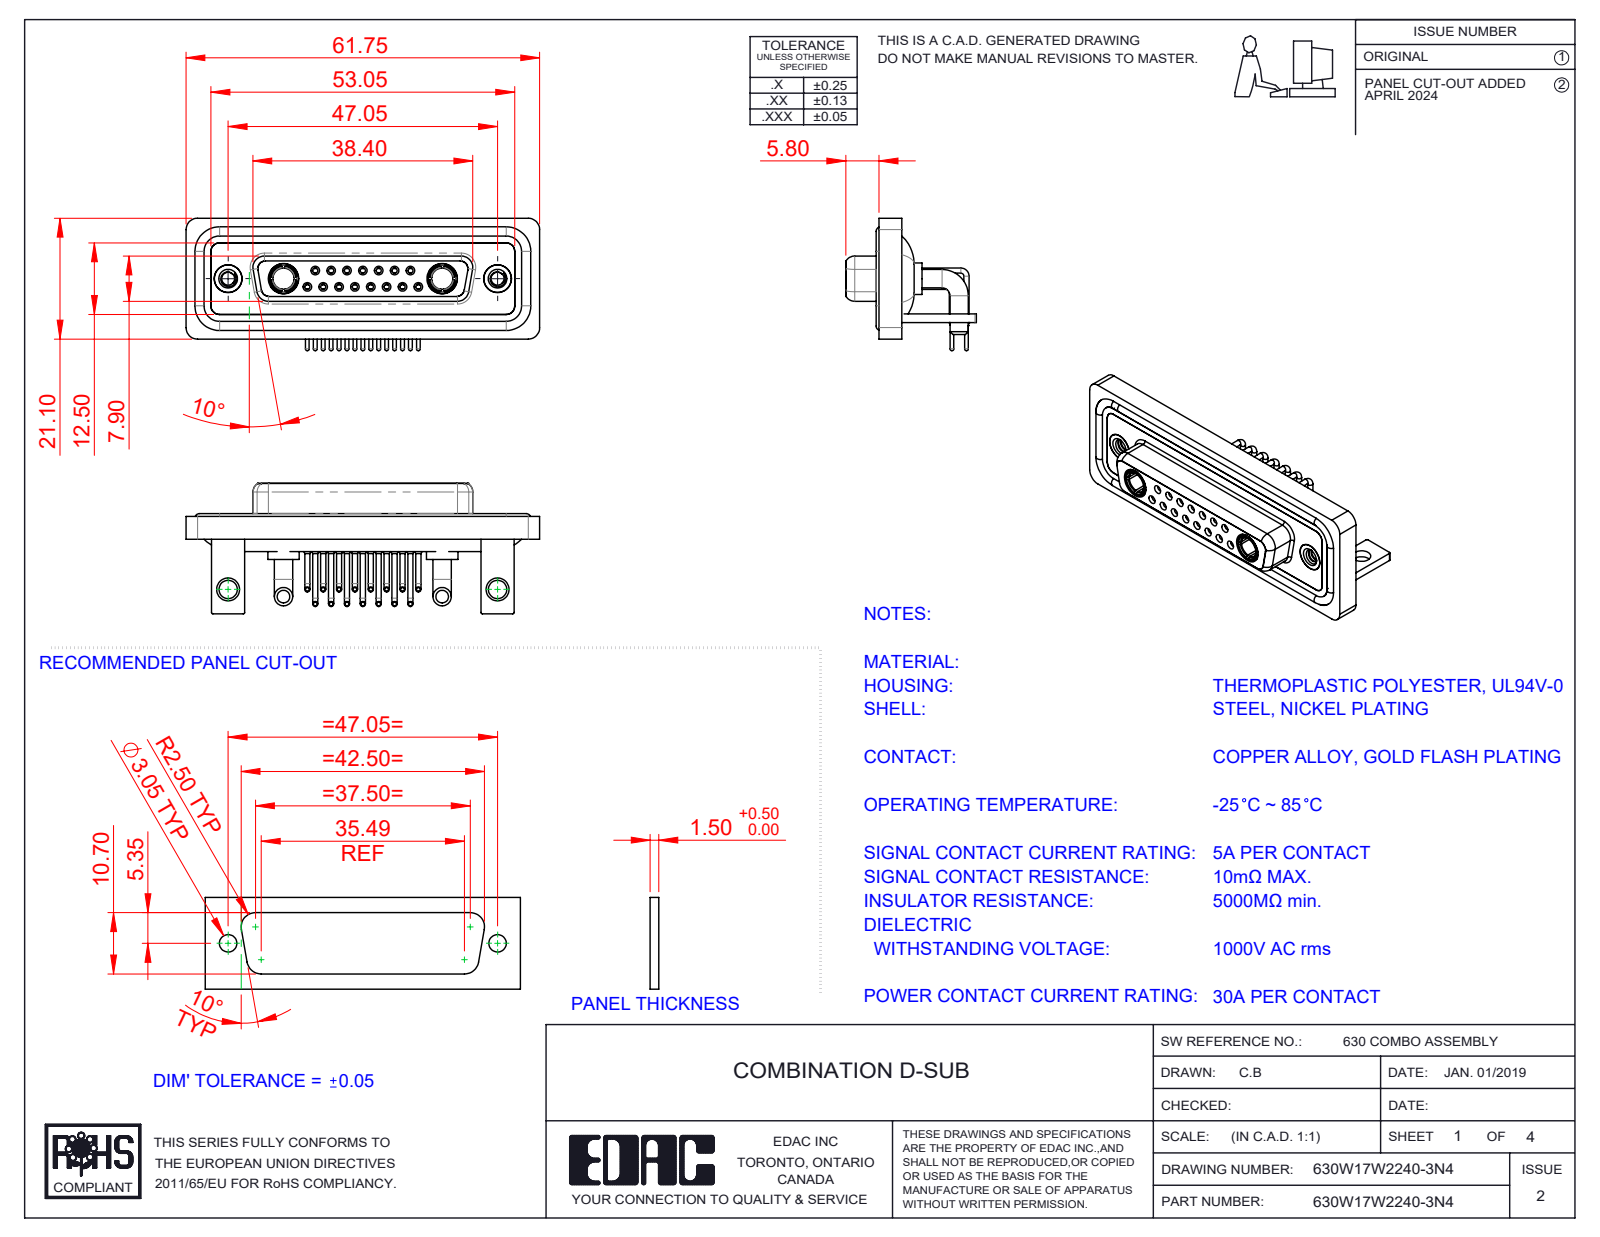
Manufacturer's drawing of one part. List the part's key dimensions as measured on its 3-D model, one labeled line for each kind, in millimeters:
Part name (STEP PRODUCT): 630Combo Shell Rear_25 Contacts; 630Combo Shell Front_25 Contacts; Power Socket_30A RA; 630Combo Contact Row 1_50 Contacts (+6 more)
STEP written by: SolidWorks 2023 (CONFIG_CONTROL_DESIGN)
Units: millimetres
Bodies: 28 solids, 1385 faces (408 planar, 607 cylindrical, 370 other)
Overall size (bounding box): 61.75 × 23.12 × 22.8
Volume: 8 909 mm³ · Surface area: 15 302 mm²
Round holes (diameter × count): ⌀0.9 ×15, ⌀1.1 ×15, ⌀1.5 ×15, ⌀2 ×15, ⌀1.6 ×8, ⌀1.7 ×7, ⌀4.85 ×4, ⌀2.26 ×2, ⌀3.2 ×2, ⌀3.7 ×2, ⌀4 ×2, ⌀4.05 ×2
Round bosses / shafts (diameter × count): ⌀0.9 ×15, ⌀0.65 ×15, ⌀1.6 ×11, ⌀3.2 ×4, ⌀5.5 ×2, ⌀5.2 ×2, ⌀4.96 ×2, ⌀4.95 ×2
Partial cylindrical surfaces — rounded edges, fillets, slot ends (radius × count): R2 ×19, R1.5 ×18, R0.25 ×16, R1.35 ×8, R1.6 ×8, R0.5 ×5, R0.6 ×4, R0.65 ×4
Main face-to-face distances: 0.4, 1.8, 2.9, 3.7, 1.5, 4.1, 1.1, 1.4, 1.6, 3.1
Hole centre spacings: 3.16, 2.77, 5.54, 8.31, 5.04, 7.49, 11.08, 5.03
